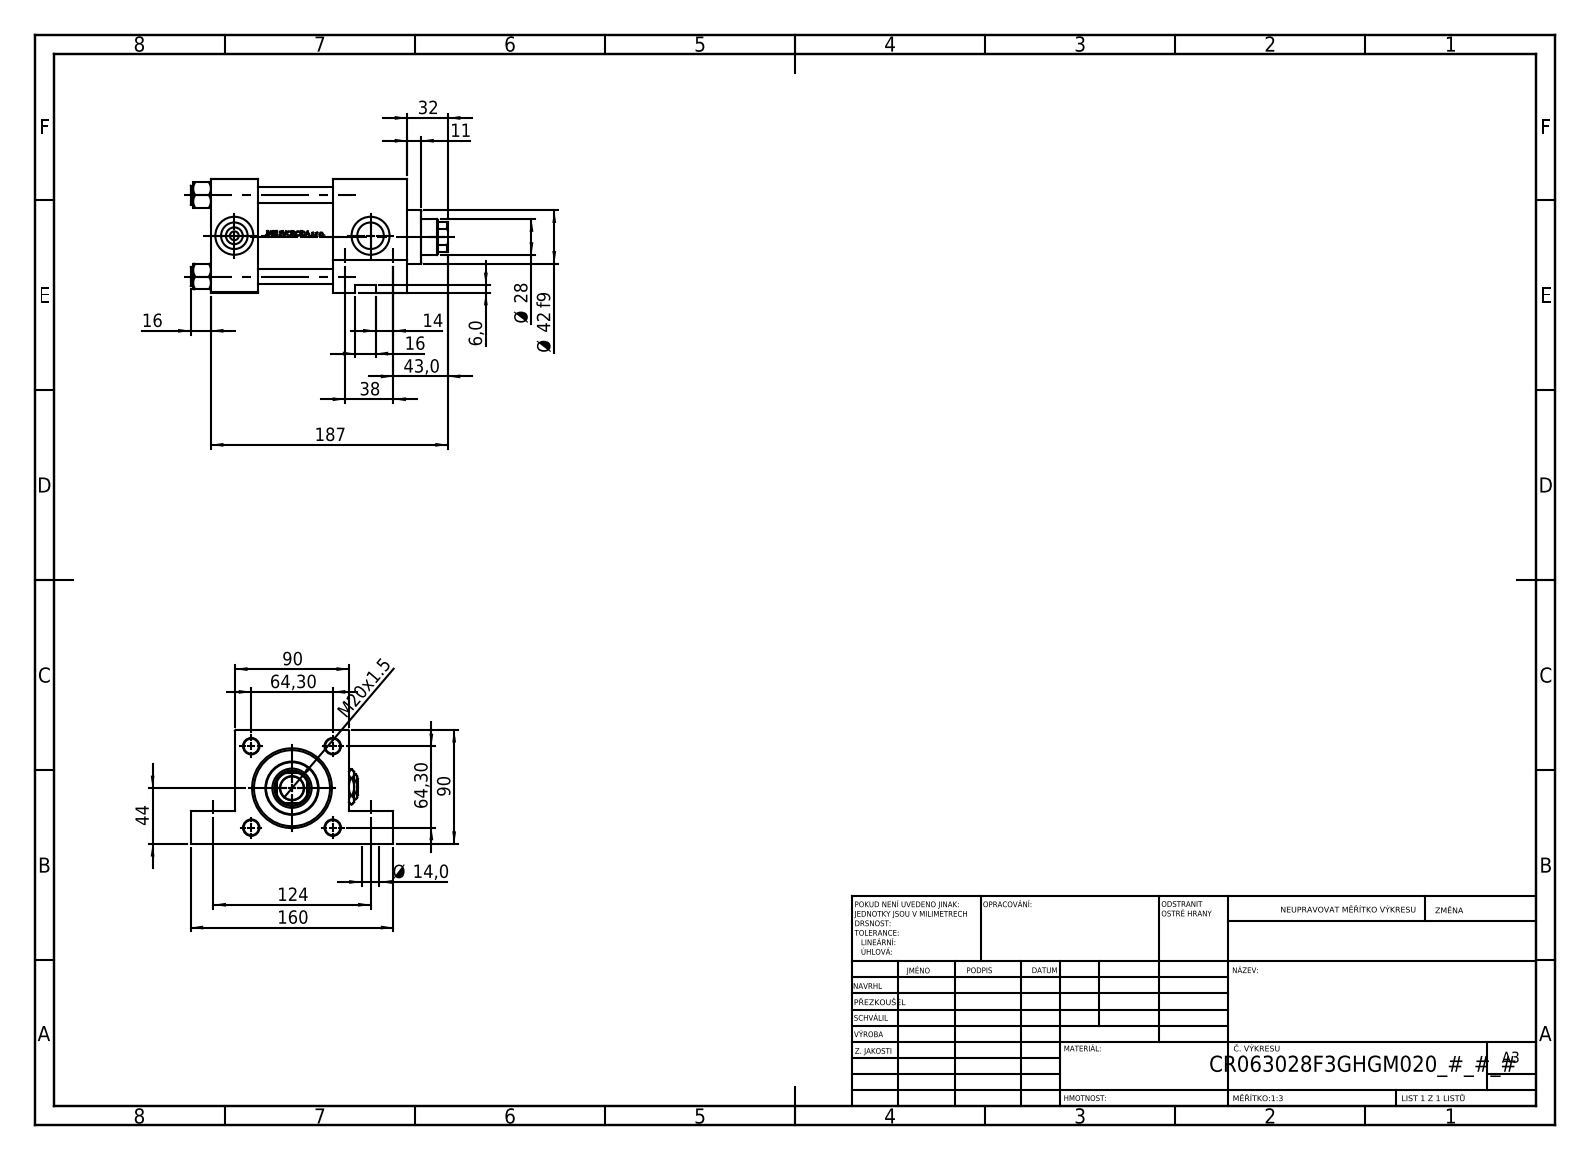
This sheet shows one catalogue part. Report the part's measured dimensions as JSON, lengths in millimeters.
{"part_name": "V215CR_VCP_F; V215CR_F_TYCINKA; V215CR_F_Body; Zatka_pro_OIL_PORT (+2 more)", "step_written_by": "SolidWorks 2019 (CONFIG_CONTROL_DESIGN)", "units": "millimeters", "bodies": {"solids": 13, "faces": 1200, "planar": 484, "cylindrical": 134, "other": 582}, "overall_size": [203, 160, 90], "volume_mm3": 1023000, "surface_area_mm2": 198658, "round_holes": [[12, 4], [20.96, 3], [30, 3], [7, 2], [14, 2], [14, 2], [18.5, 1], [20, 1], [28, 1], [31, 1], [50, 1], [60, 1]], "round_bosses_or_shafts": [[15, 4], [69, 1], [42, 1]], "partial_cylinders_radius": [[13.5, 1]], "face_to_face_distances": [90, 59, 37, 118, 155, 96, 20, 26, 64, 125], "hole_center_spacings": [64.3, 38, 44.77, 46.18, 90.93, 124, 129.69, 10]}
